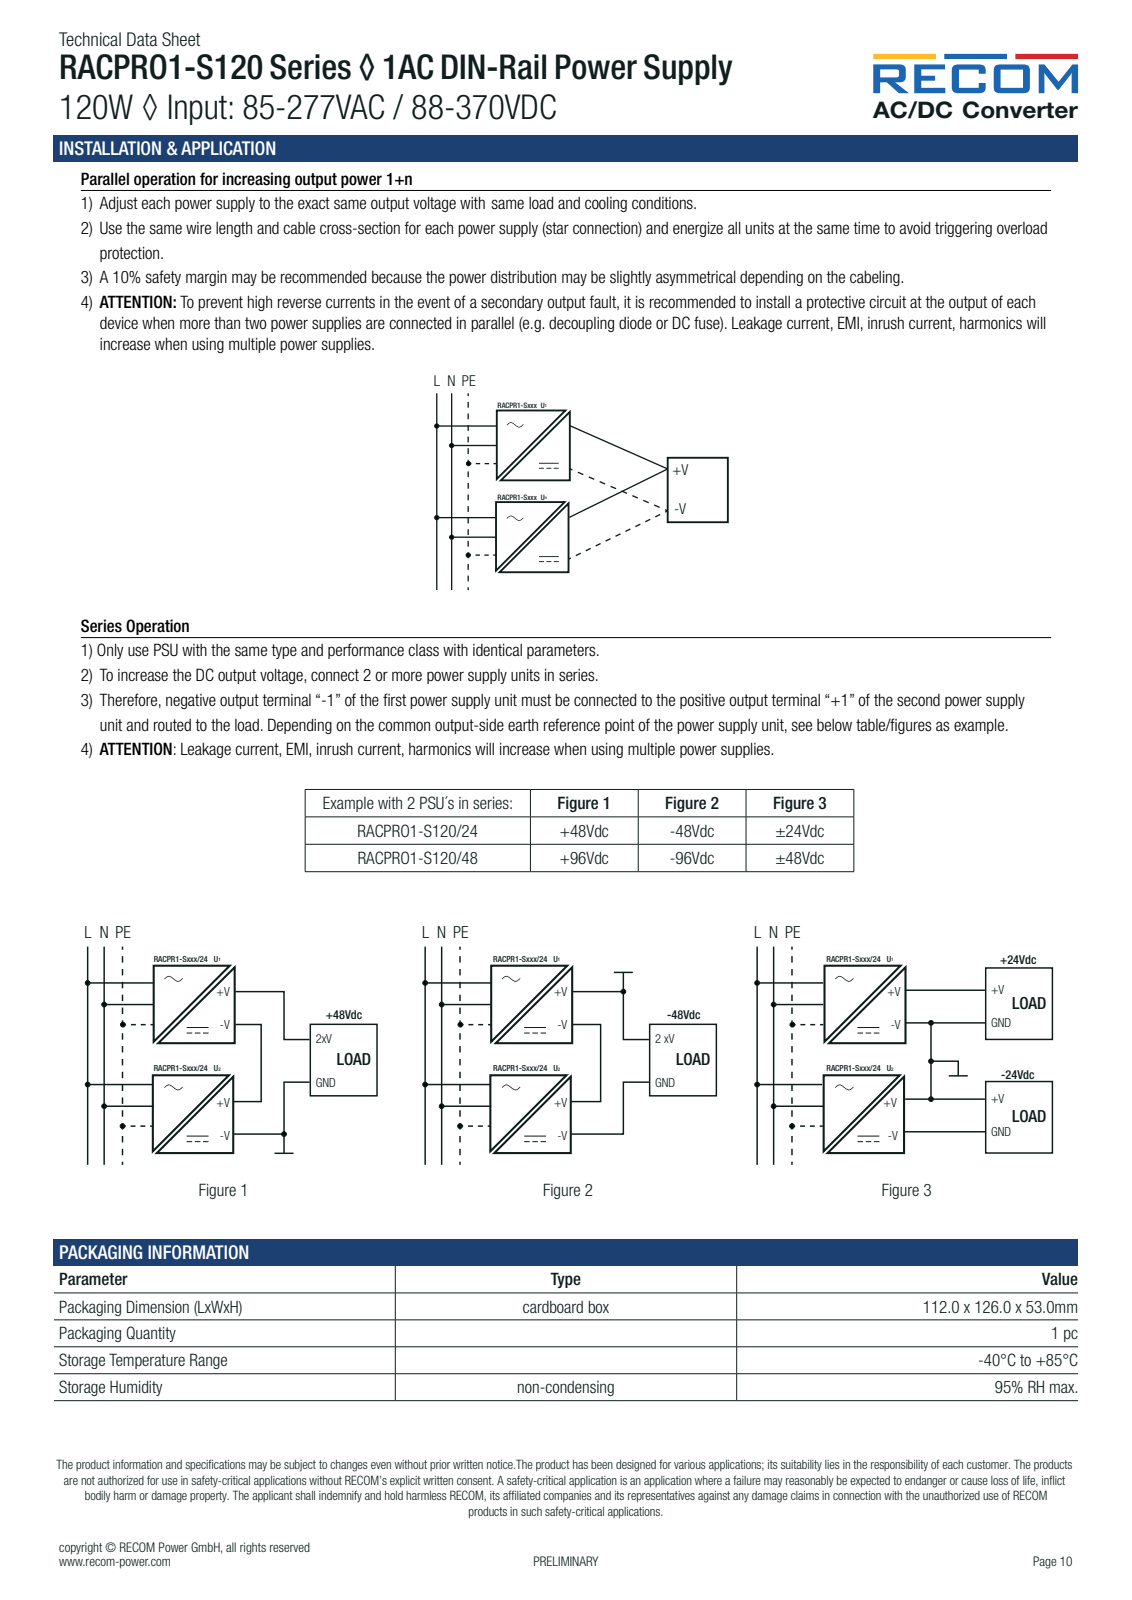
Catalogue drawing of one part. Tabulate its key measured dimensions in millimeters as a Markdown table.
| quantity | value |
| --- | --- |
| part name | SMD_1206_R_main.step_1.STEP; ThermalPin_SMD_IC_VQFN-20_R_main.step_1.STEP; SOT-89-3_main.step_1.STEP; Body-6_SMD_IC_VQFN-20_R_main.step_1.STEP (+8 more) |
| STEP written by | SolidWorks 2024 (AUTOMOTIVE_DESIGN) |
| units | millimeters |
| bodies | 262 solids, 8159 faces (5210 planar, 1917 cylindrical, 1032 other) |
| overall size | 118.59 × 100 × 28 |
| volume | 73 561 mm³ |
| surface area | 128 806 mm² |
| round holes (diameter × count) | 1.2 × 19, 1 × 16, 2.1 × 14, 0.9 × 8, 2.4 × 7, 1.5 × 6, 0.4 × 4, 1.12 × 3, 1.3 × 3, 2.5 × 3, 0.7 × 2, 0.94 × 2 |
| round bosses / shafts (diameter × count) | 1.4 × 13, 1.35 × 12, 0.6 × 8, 3 × 2, 0.88 × 2, 5.56 × 1, 5.5 × 1, 5 × 1 |
| partial cylindrical surfaces (radius × count) | 0.1 × 126, 0.25 × 98, 0.3 × 75, 0.5 × 32, 0.15 × 24, 0.2 × 20, 1 × 18, 0.8 × 15 |
| main face-to-face distances | 1.25, 1.55, 26.45, 26.75, 25.2, 1, 0.55, 27, 25.45, 25.75 |
| hole center spacings | 5, 10, 5.08, 22.9, 29.15, 1.2, 6.2, 6.21 |
